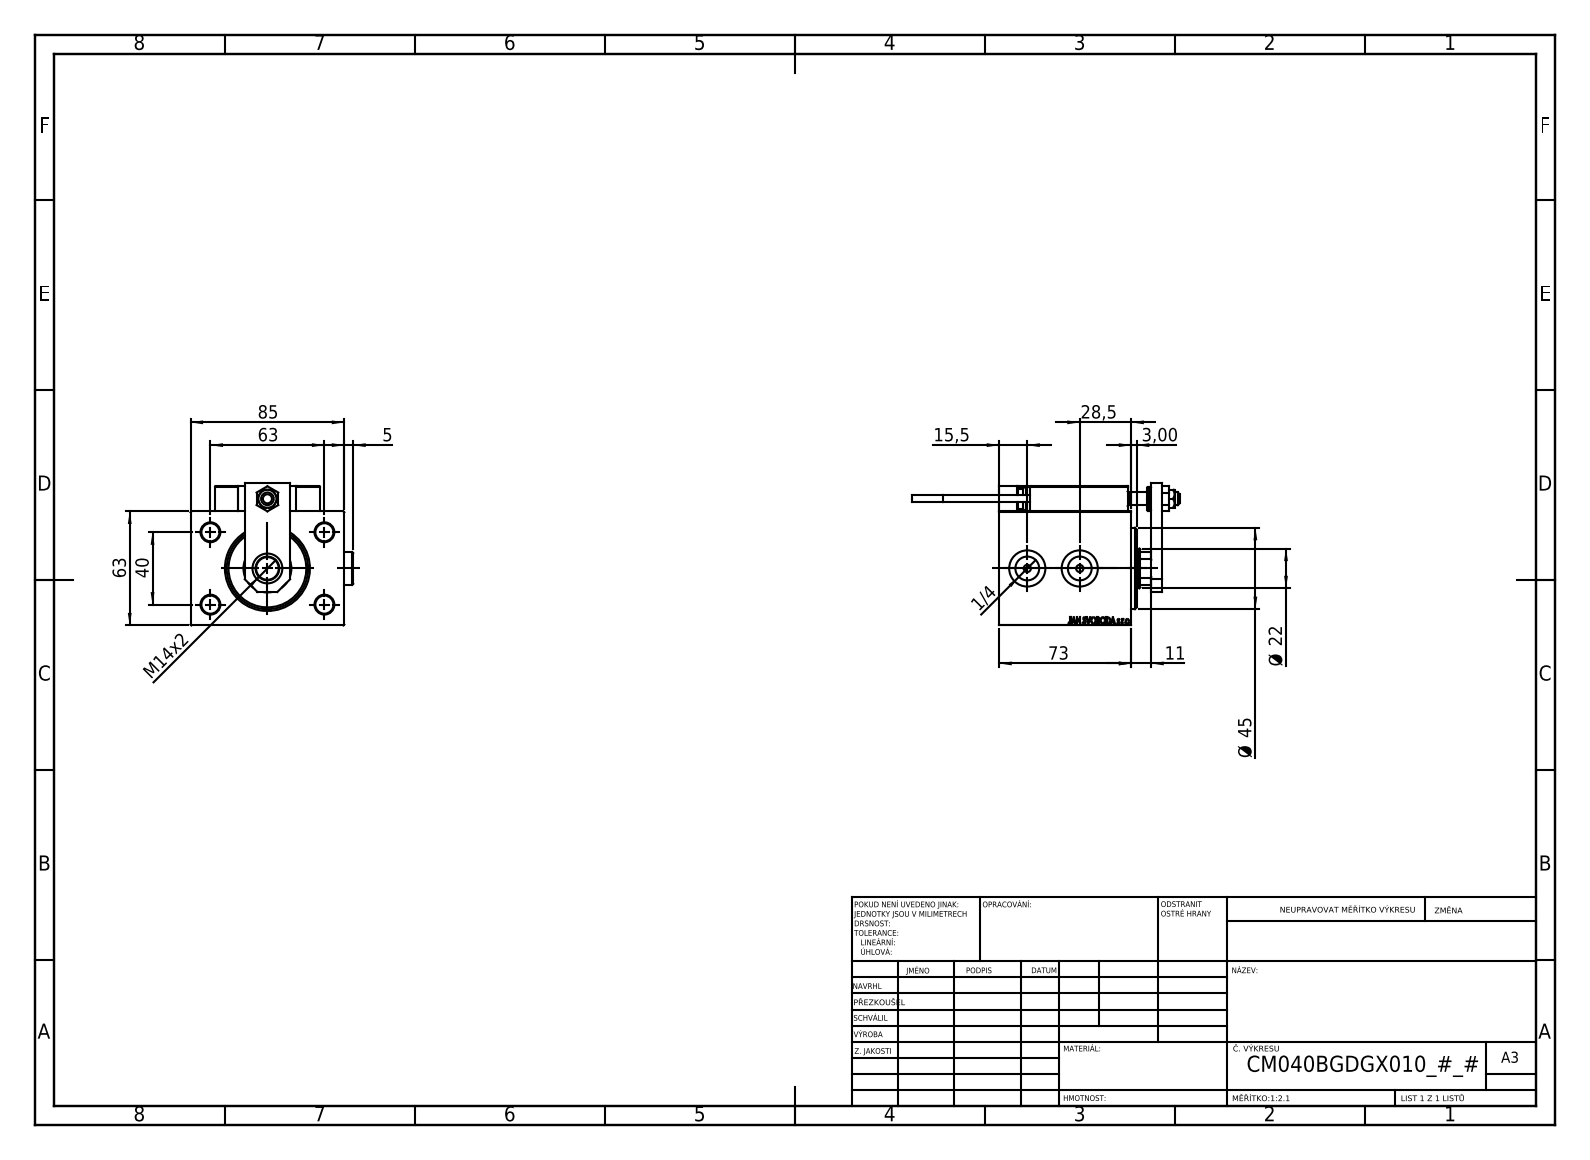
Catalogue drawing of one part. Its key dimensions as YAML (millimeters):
part_name: "Block; SWITCH DIM B,W; ALLEN BOLT D8; ALLEN BOLT D5 (+8 more)"
step_written_by: "SolidWorks 2019 (CONFIG_CONTROL_DESIGN)"
units: millimeters
bodies: {solids: 26, faces: 1370, planar: 595, cylindrical: 198, other: 577}
overall_size: [147.7, 89.9, 78.5]
volume: 415609
surface_area: 89222
round_holes:
  - {diameter: 4, count: 6}
  - {diameter: 8, count: 5}
  - {diameter: 3.2, count: 4}
  - {diameter: 10, count: 4}
  - {diameter: 5, count: 2}
  - {diameter: 13.16, count: 2}
  - {diameter: 20, count: 2}
  - {diameter: 7, count: 1}
  - {diameter: 12.5, count: 1}
  - {diameter: 16.5, count: 1}
  - {diameter: 22, count: 1}
  - {diameter: 25.5, count: 1}
round_bosses_or_shafts:
  - {diameter: 18, count: 2}
  - {diameter: 5, count: 2}
  - {diameter: 3.8, count: 2}
  - {diameter: 13, count: 1}
  - {diameter: 11, count: 1}
partial_cylinders:
  - {radius: 0.3, count: 30}
  - {radius: 3, count: 2}
  - {radius: 10.5, count: 1}
face_to_face_distances: [63, 85, 73, 22, 14, 51, 10, 77, 17, 51.4]
hole_center_spacings: [37.31, 11.37, 20, 25.08, 29.59, 29.69, 33.3, 35.57]
